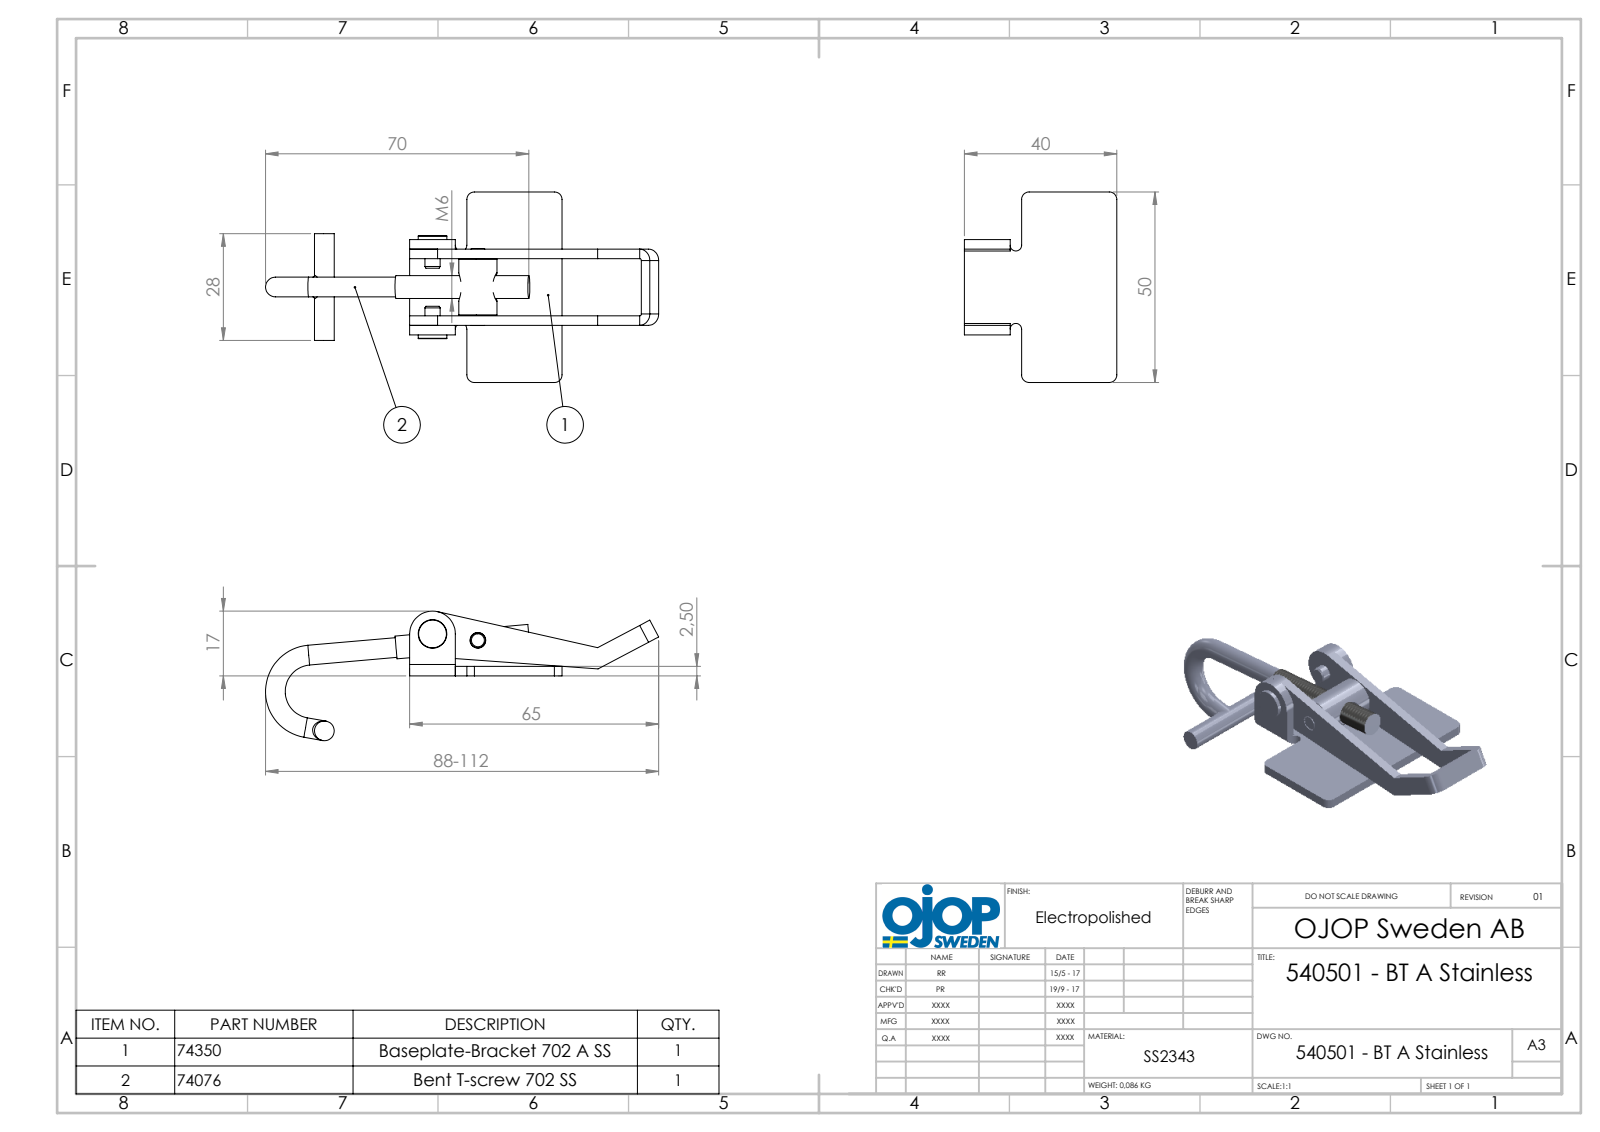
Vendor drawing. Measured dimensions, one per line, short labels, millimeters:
name: 702 - A; 702 - Bygel; 702 - Ansatsnit; 702 - Rulle (+2 more)
written by: SolidWorks 2015 (AUTOMOTIVE_DESIGN)
unit: mm
bodies: 6 solids, 137 faces (58 planar, 59 cylindrical, 20 other)
size: 106.12 × 50 × 25.58
volume: 11 407 mm³; area: 10 681 mm²
holes: 2× ⌀4.1, 2× ⌀5
bosses: 3× ⌀5.18, 2× ⌀6, 2× ⌀4, 1× ⌀10, 1× ⌀7.5
rounds: 4× R0.5, 4× R2, 4× R3, 2× R1.5, 1× R6
face distances: 2.5, 17.5, 20, 15, 5, 22.5, 25, 12.5, 35, 32.5
hole spacings: 12.03
